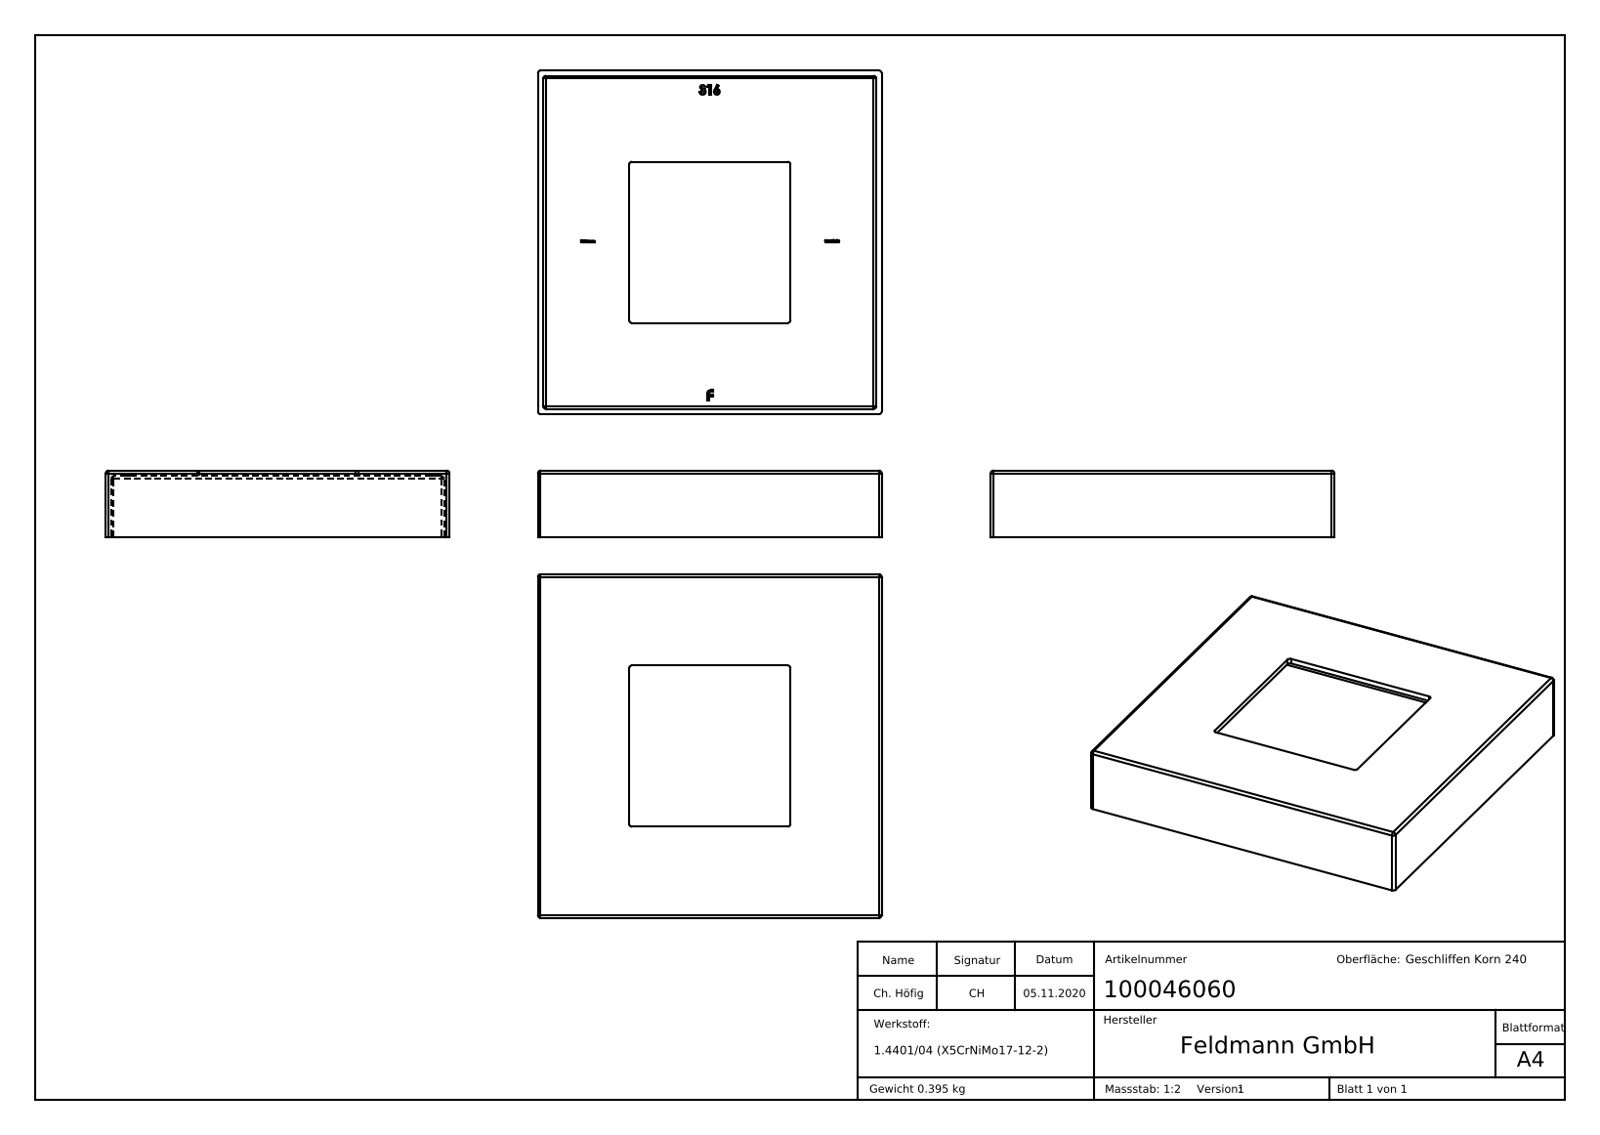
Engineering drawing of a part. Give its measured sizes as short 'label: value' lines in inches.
name: 100046060
written by: SolidWorks 2018 (CONFIG_CONTROL_DESIGN)
unit: in
bodies: 1 solid, 311 faces (149 planar, 20 cylindrical, 142 other)
size: 5.079 × 5.079 × 0.984
volume: 3.01 in³; area: 78.02 in²
rounds: 20× R0.039
face distances: 0.079, 5, 5.079, 4.921, 0.906, 0.984, 1.348, 3.73, 1.27, 3.652
